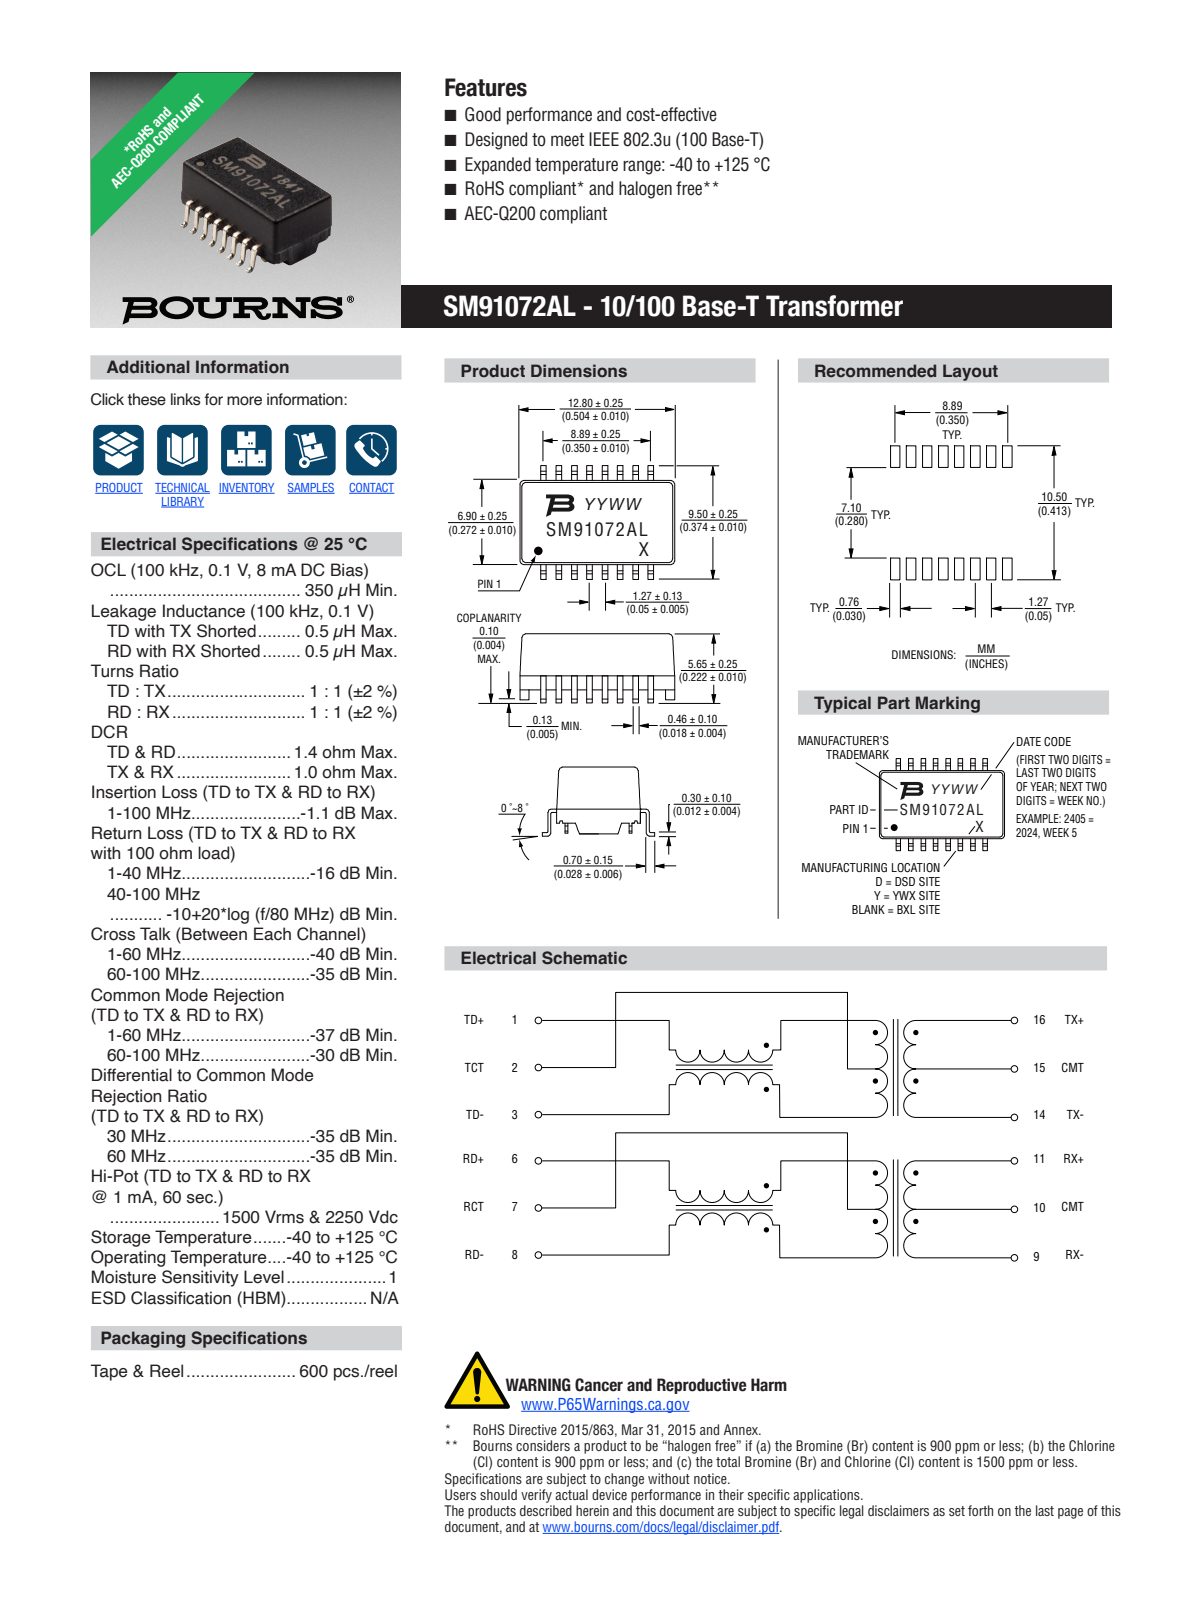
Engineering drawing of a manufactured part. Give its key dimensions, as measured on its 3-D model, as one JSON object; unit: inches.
{"part_name": "16pin_case_171102_asm; 16PIN_CASE_171102; 16PIN_CASE_PIN", "step_written_by": "Autodesk Inventor 2017 (AUTOMOTIVE_DESIGN)", "units": "inches", "bodies": {"solids": 17, "faces": 1152, "planar": 539, "cylindrical": 331, "other": 282}, "overall_size": [0.504, 0.372, 0.222], "volume_in3": 0.012, "surface_area_in2": 1.04, "round_holes": [[0.047, 1]], "partial_cylinders_radius": [[0.017, 16], [0.012, 12], [0.004, 6], [0.014, 6], [0.008, 4]], "face_to_face_distances": [0.045, 0.031, 0.024, 0.218, 0.059, 0.267, 0.05, 0.032, 0.037, 0.235]}
